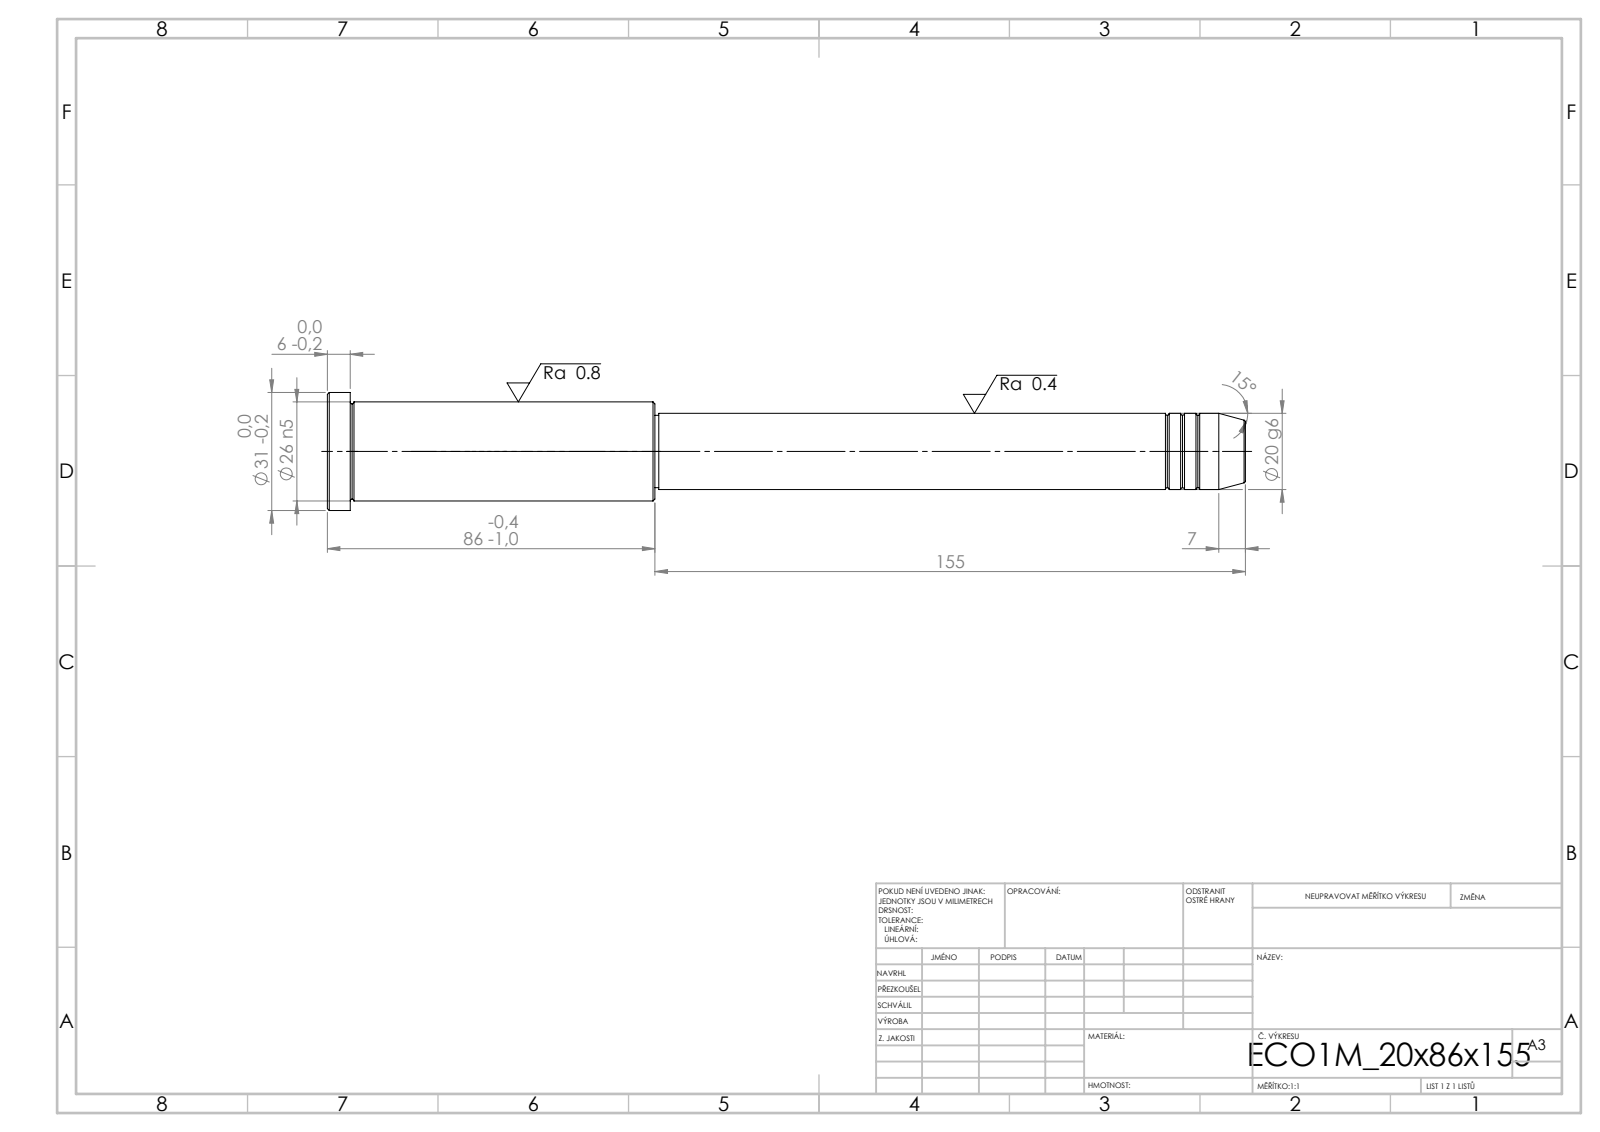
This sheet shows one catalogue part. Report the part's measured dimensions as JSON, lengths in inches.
{"step_written_by": "SolidWorks 2019 (CONFIG_CONTROL_DESIGN)", "units": "inches", "bodies": {"solids": 1, "faces": 43, "planar": 5, "cylindrical": 14, "other": 24}, "overall_size": [9.488, 1.22, 1.22], "volume_in3": 5.807, "surface_area_in2": 28.48, "round_bosses_or_shafts": [[1.22, 1], [1.024, 1], [0.787, 1], [0.748, 1]], "face_to_face_distances": [0.236, 3.15, 3.386, 6.102, 9.252, 9.488, 6.063, 0.039, 3.189, 3.425]}
